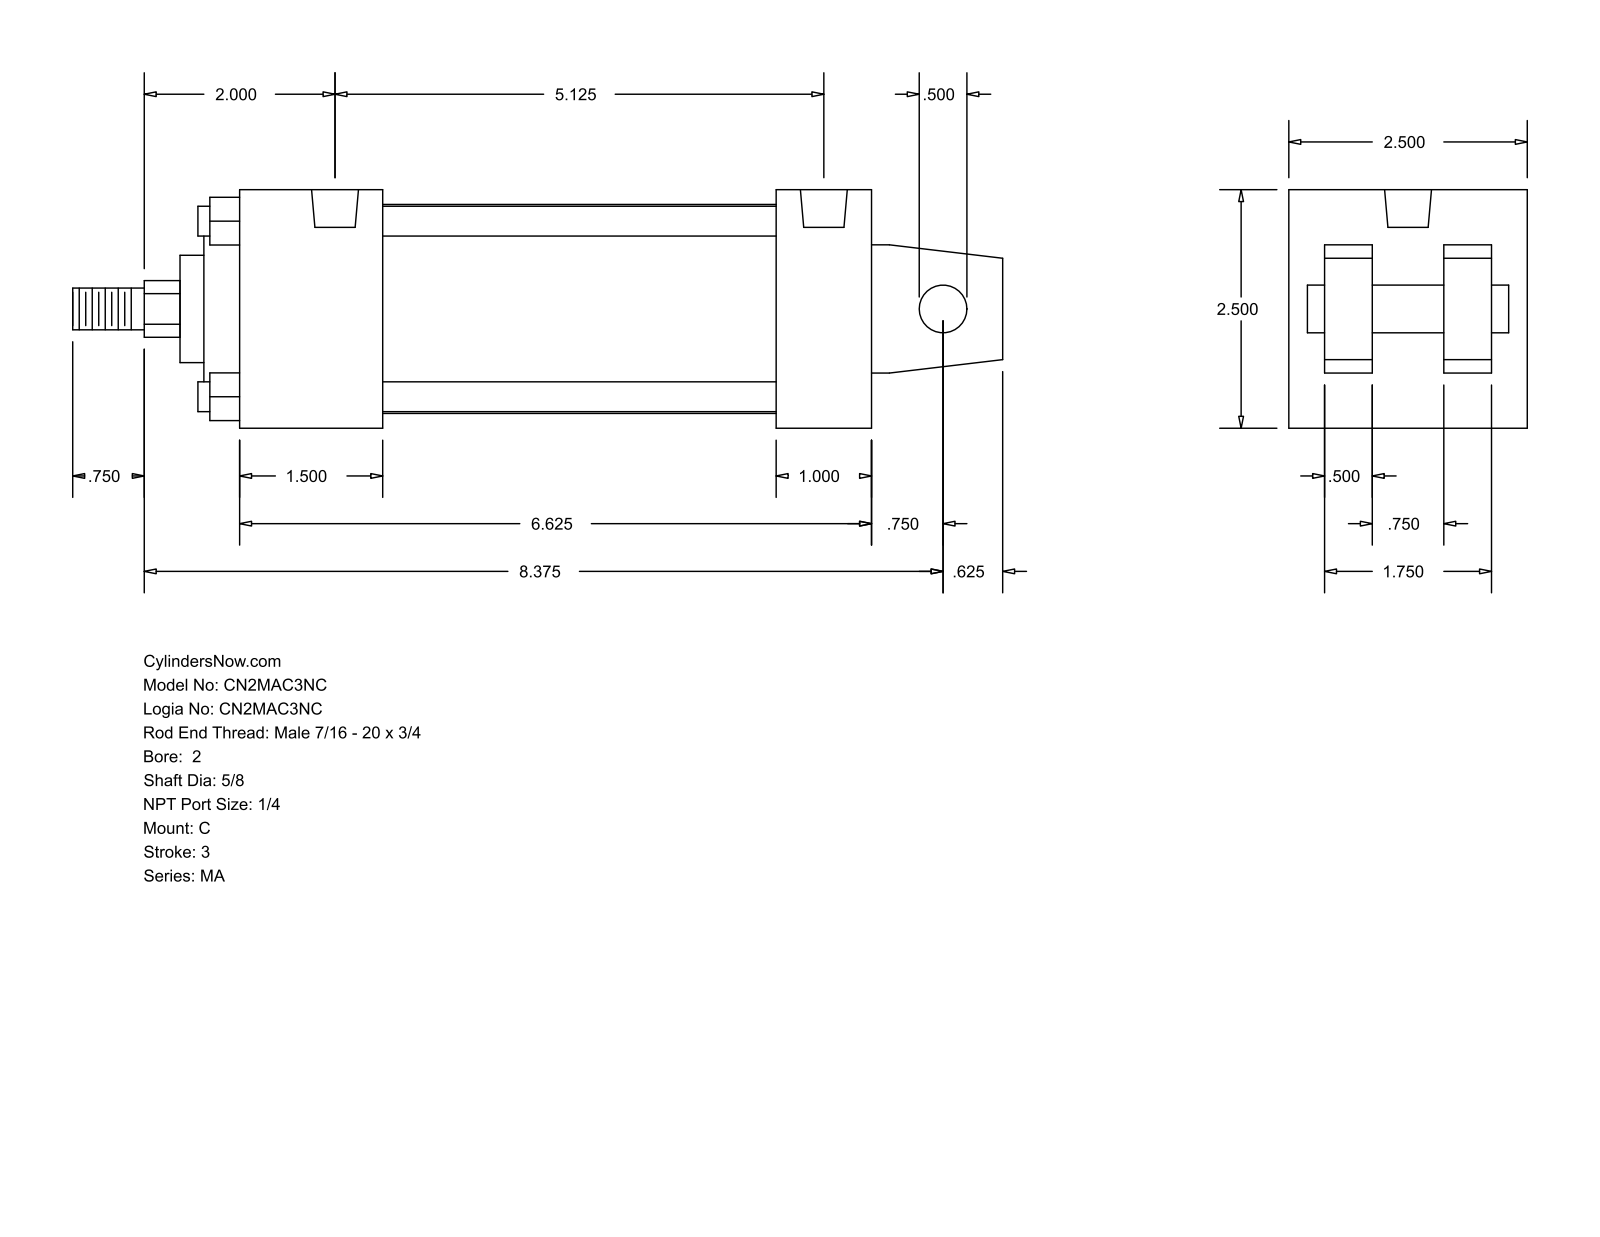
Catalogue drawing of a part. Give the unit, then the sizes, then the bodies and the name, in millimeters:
Units: millimetres
Overall size (bounding box): 247.65 × 63.5 × 63.5
Round holes (diameter × count): ⌀7.94 ×4, ⌀12.49 ×2
Round bosses / shafts (diameter × count): ⌀7.94 ×4, ⌀55.63 ×1, ⌀50.8 ×1, ⌀28.57 ×1, ⌀15.88 ×1, ⌀12.7 ×1, ⌀11.11 ×1
Partial cylindrical surfaces — rounded edges, fillets, slot ends (radius × count): R7.54 ×1
Main face-to-face distances: 63.5, 9.52, 12.7, 22.22, 41.28, 53.98, 31.76, 25.4, 38.1, 168.28
Hole centre spacings: 130.17
Bodies: 0 solids, 105 faces (77 planar, 28 cylindrical, 0 other)
Part name (STEP PRODUCT): MA_C__0200_0.625
STEP written by: GSSL Pune (CONFIG_CONTROL_DESIGN)
